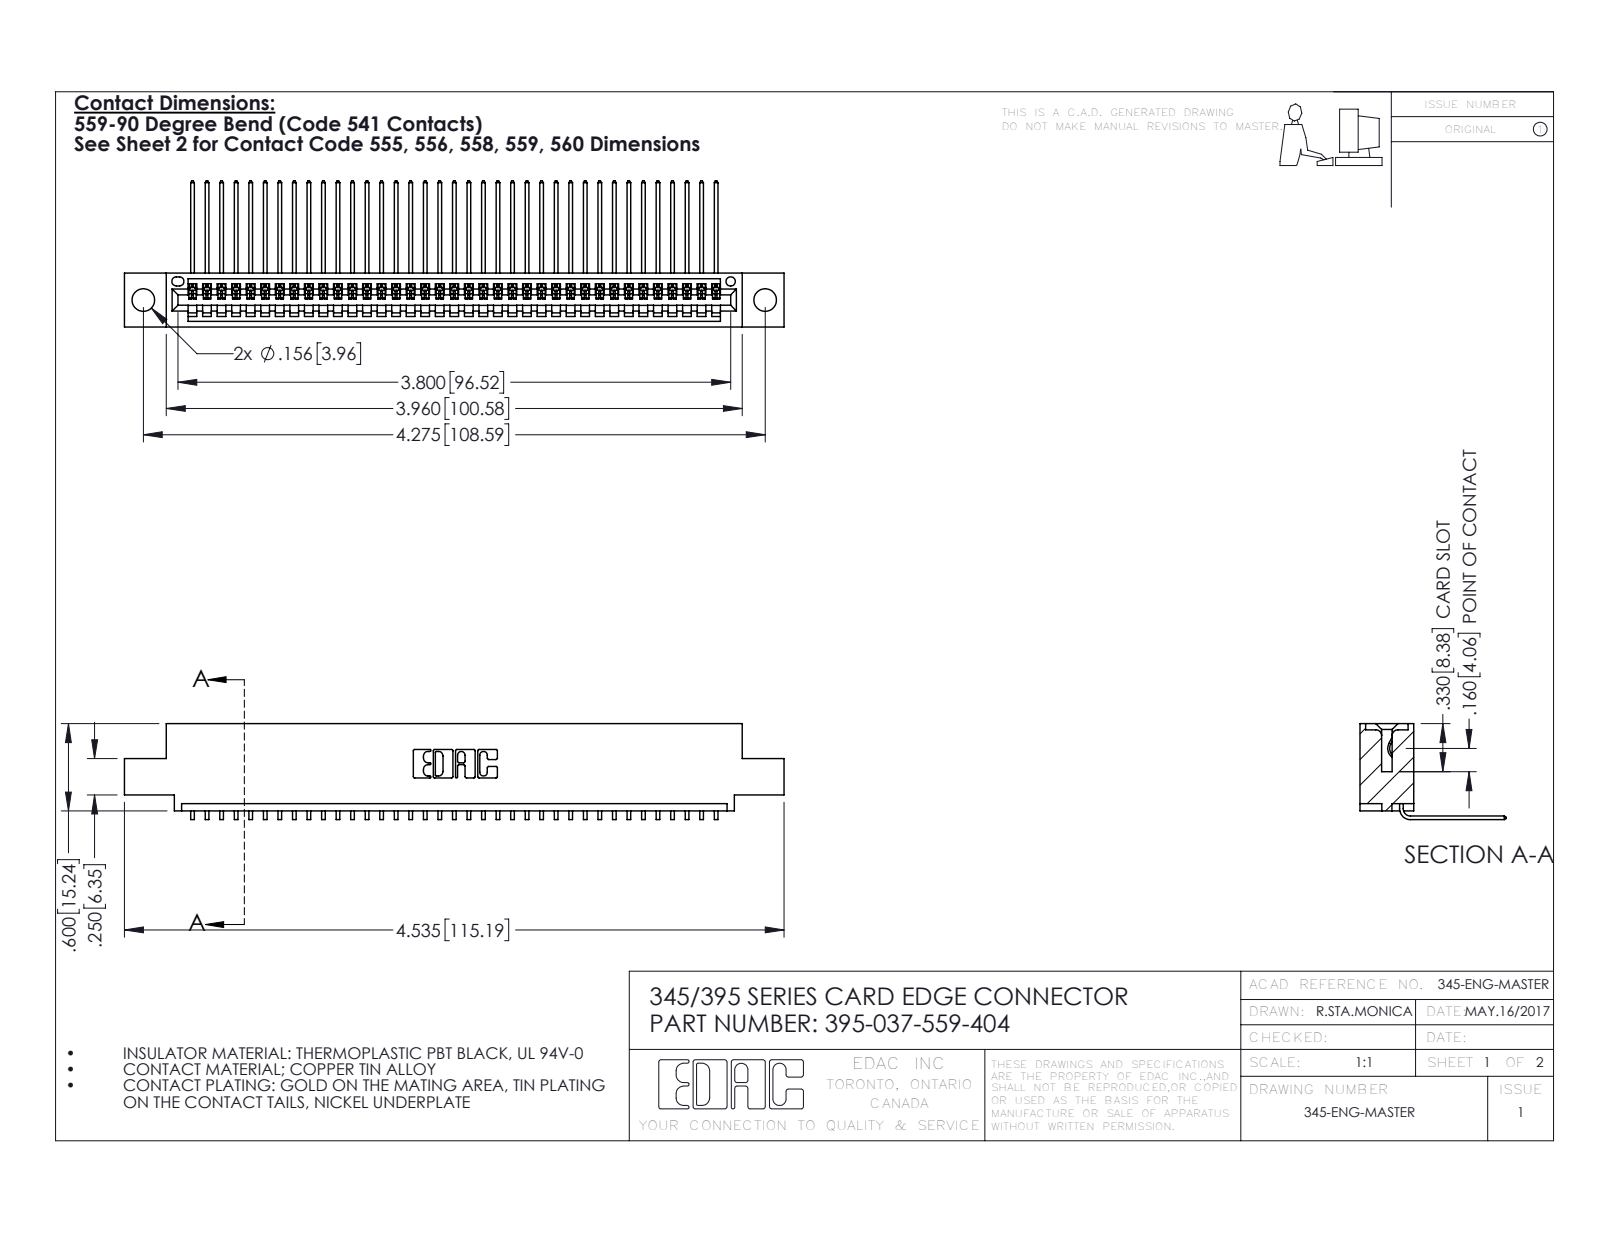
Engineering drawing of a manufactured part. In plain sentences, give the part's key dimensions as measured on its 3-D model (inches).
The part is named "345-292-001_558 559 Tail - 1; 345 Part_0.110 Offset - 0.156 Dia-TH; 395-037-559-404". Its 3-D file was written by "SolidWorks 2016 (CONFIG_CONTROL_DESIGN)". It is 38 solids with 2350 faces: 1638 planar, 712 cylindrical and 0 other. Overall it measures 4.535 by 1.005 by 0.659 inches. Its volume is 0.663 cubic inches and its surface area 23.22 square inches. Round holes: 2 of diameter 0.156, 1 of diameter 0.064. Partial cylindrical surfaces (rounded edges, fillets, slot ends): 74 of radius 0.006, 22 of radius 0.01, 6 of radius 0.007, 6 of radius 0.031, 3 of radius 0.026, 2 of radius 0.031, 2 of radius 0.04, 1 of radius 0.014. The main face-to-face distances are 0.072, 0.298, 0.37, 0.2, 0.098, 0.272, 0.025, 0.225, 0.149, 0.072. The hole center spacings are 0.27, 4.039, 4.275.
